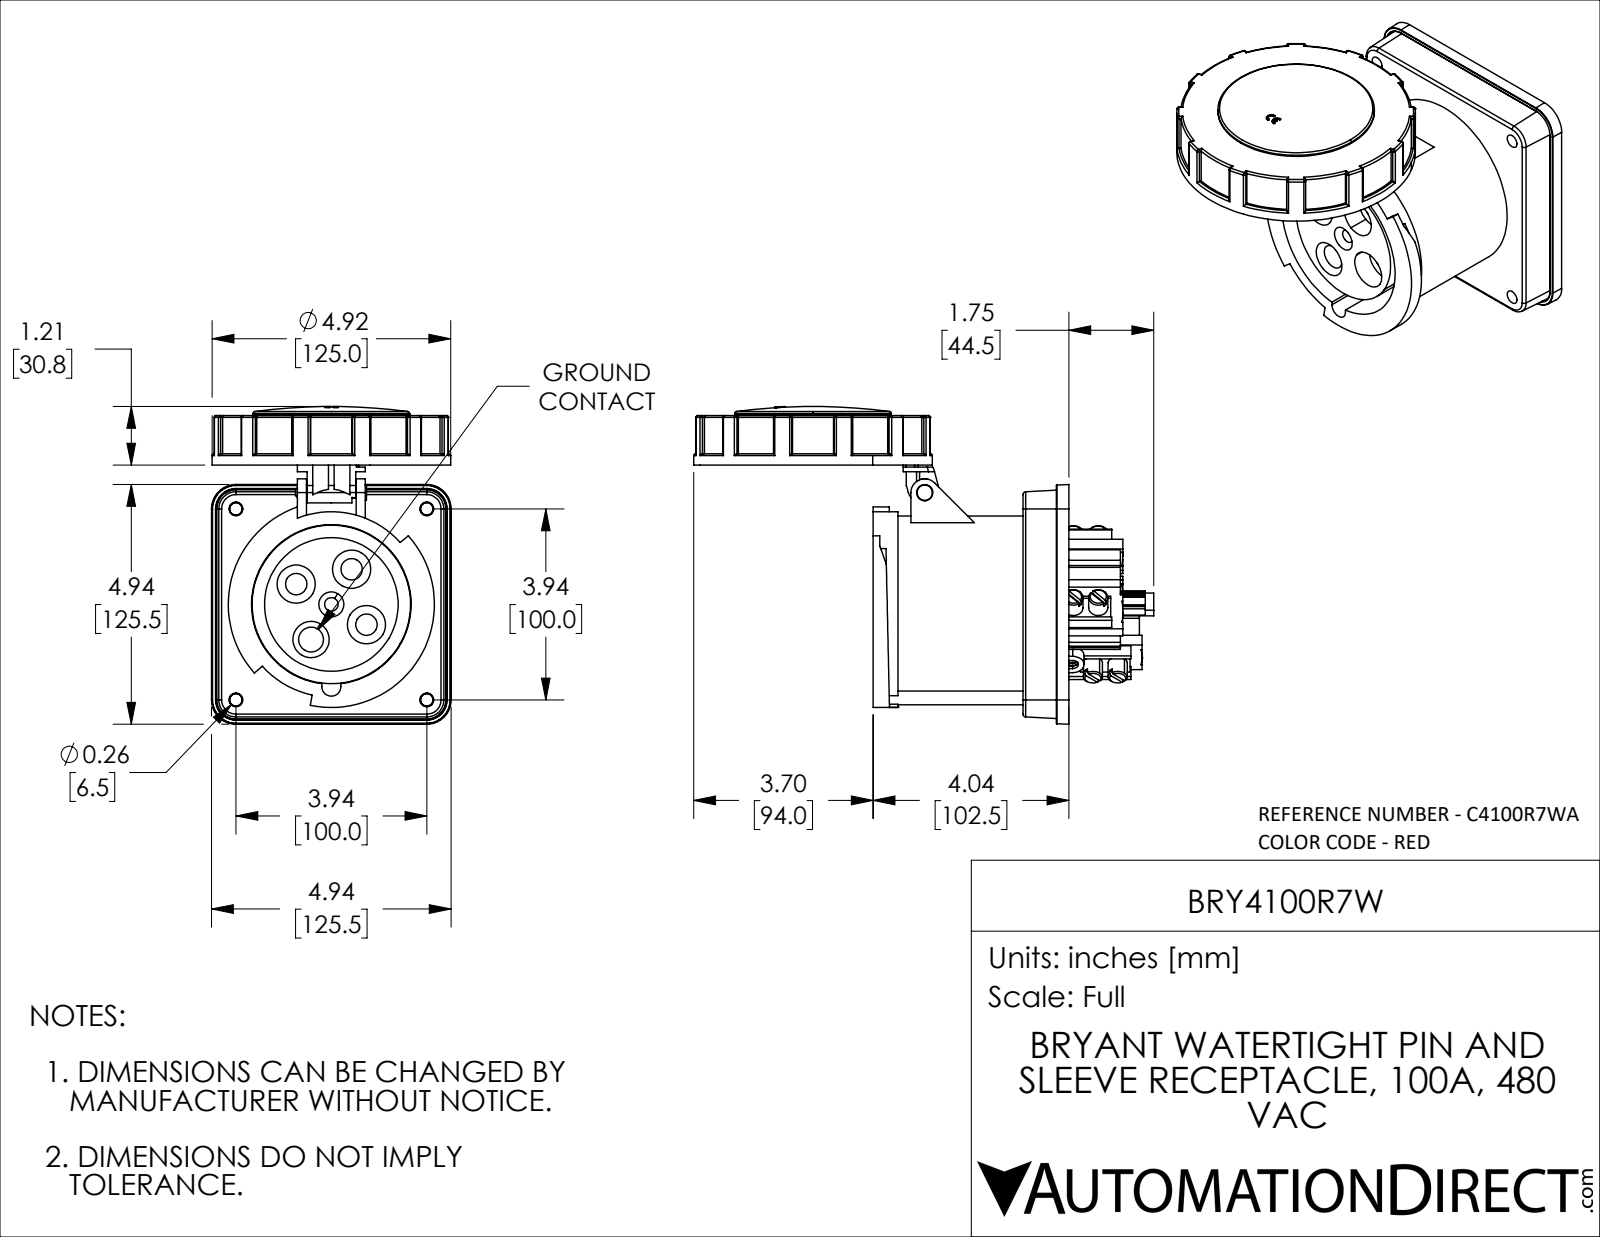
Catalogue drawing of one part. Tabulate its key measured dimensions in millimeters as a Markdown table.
| quantity | value |
| --- | --- |
| part name | BRY4100R7W |
| STEP written by | SolidWorks 2021 (CONFIG_CONTROL_DESIGN) |
| units | millimeters |
| bodies | 2 solids, 974 faces (447 planar, 361 cylindrical, 166 other) |
| overall size | 241 × 166.4 × 125.5 |
| volume | 1 082 000 mm³ |
| surface area | 182 435 mm² |
| round holes (diameter × count) | 7.2 × 4, 11.2 × 3, 20 × 3, 5.1 × 1, 7.1 × 1, 8.5 × 1, 13 × 1, 83.6 × 1, 84 × 1, 85 × 1, 115 × 1 |
| round bosses / shafts (diameter × count) | 10 × 8, 125 × 1, 97 × 1, 92.6 × 1, 83 × 1, 82 × 1, 80.5 × 1, 70 × 1 |
| partial cylindrical surfaces (radius × count) | 1 × 55, 2 × 18, 2.5 × 10, 0.25 × 8, 3 × 7, 5 × 6, 0.5 × 5, 1.5 × 4 |
| main face-to-face distances | 24, 26, 3.5, 2, 102.5, 78.5, 4, 20, 99, 75 |
| hole center spacings | 21.25, 30.05, 50.48, 68.37, 70.71, 78.92, 91.4, 100 |
